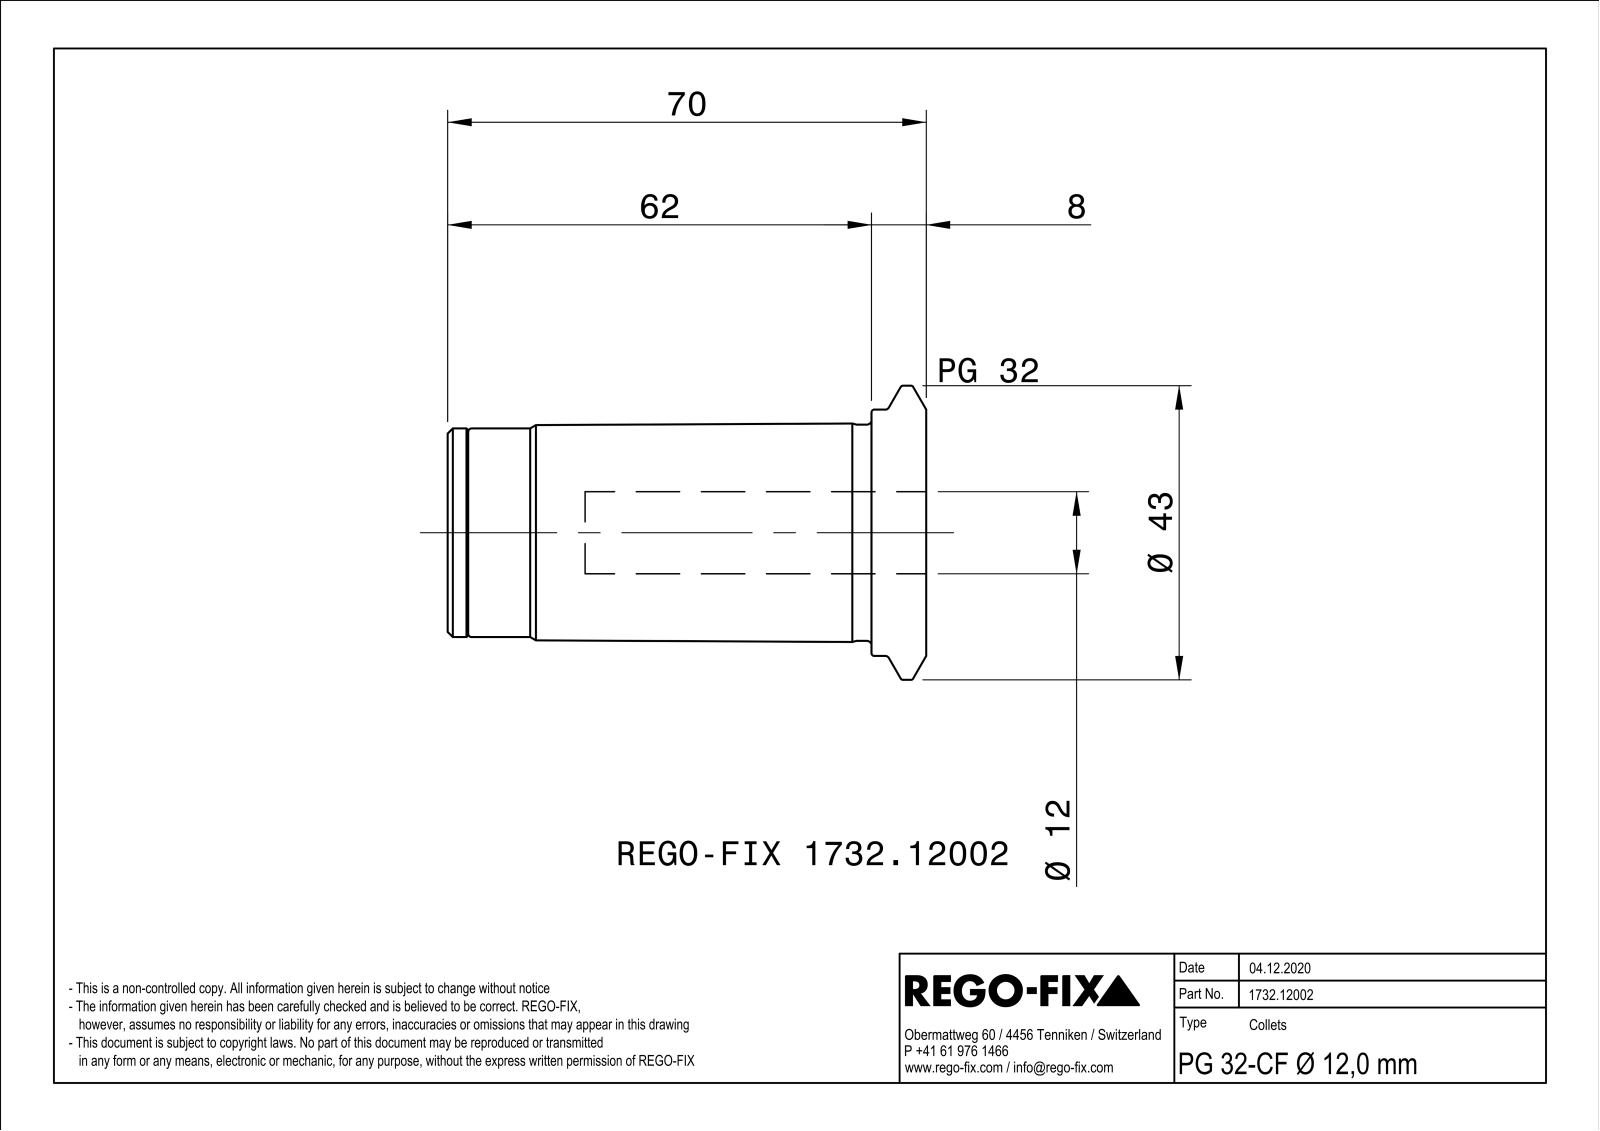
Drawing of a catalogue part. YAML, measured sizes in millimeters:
part_name: "NOCUT"
step_written_by: "SIEMENS PLM Software Solid Edge ST10 (AUTOMOTIVE_DESIGN)"
units: millimeters
bodies: {solids: 1, faces: 132, planar: 31, cylindrical: 46, other: 55}
overall_size: [70, 43, 42.99]
volume: 45349
surface_area: 16787
round_holes:
  - {diameter: 4, count: 3}
  - {diameter: 8.92, count: 1}
  - {diameter: 10.5, count: 1}
  - {diameter: 12, count: 1}
  - {diameter: 15.5, count: 1}
  - {diameter: 26.92, count: 1}
  - {diameter: 28.5, count: 1}
round_bosses_or_shafts:
  - {diameter: 43, count: 1}
  - {diameter: 36, count: 1}
  - {diameter: 31.6, count: 1}
  - {diameter: 30.5, count: 1}
  - {diameter: 26.5, count: 1}
  - {diameter: 21, count: 1}
partial_cylinders:
  - {radius: 2, count: 6}
  - {radius: 1, count: 3}
  - {radius: 3.5, count: 3}
  - {radius: 3.98, count: 1}
  - {radius: 4.75, count: 1}
  - {radius: 8.75, count: 1}
face_to_face_distances: [1, 70, 58, 12, 59, 11, 8, 60, 2, 10]
hole_center_spacings: [7.75, 13.42, 13.43]
